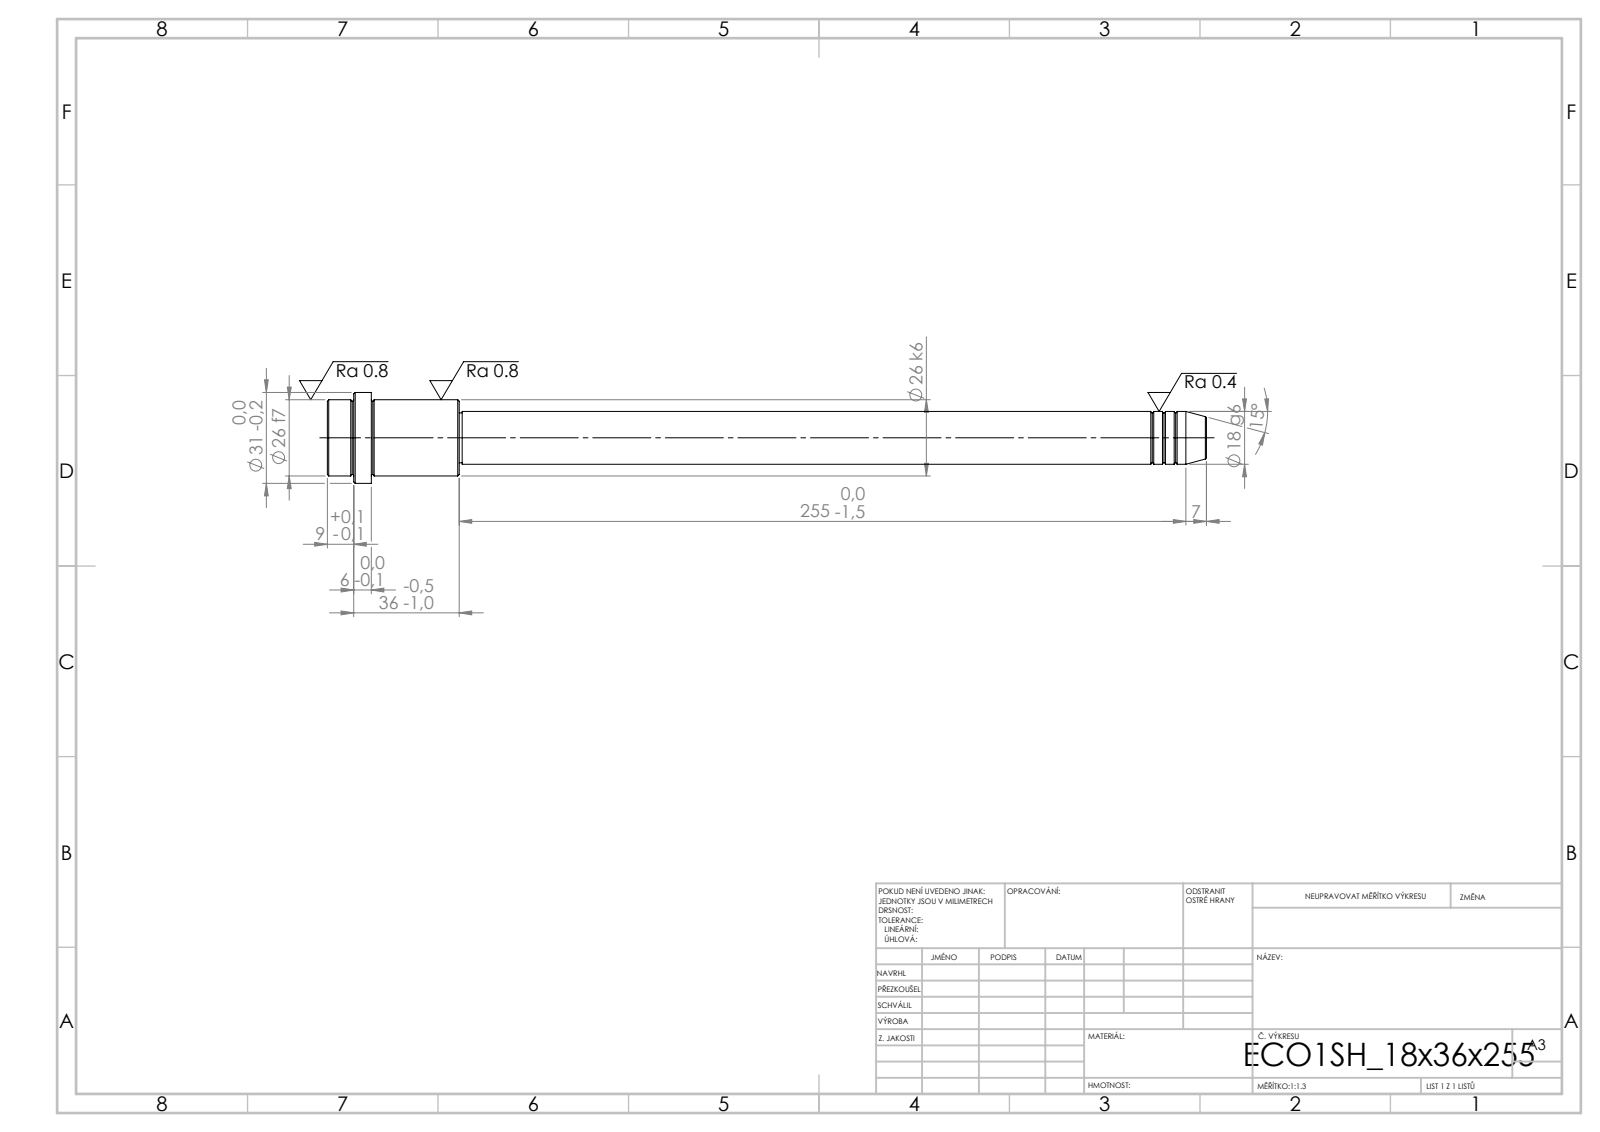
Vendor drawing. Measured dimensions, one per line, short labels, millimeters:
written by: SolidWorks 2019 (CONFIG_CONTROL_DESIGN)
unit: mm
bodies: 1 solid, 52 faces (6 planar, 16 cylindrical, 30 other)
size: 300 × 31 × 31
volume: 89 590 mm³; area: 19 719 mm²
bosses: 1× ⌀31, 1× ⌀26, 1× ⌀18, 1× ⌀17
face distances: 45, 30, 15, 36, 6, 9, 255, 285, 291, 300
